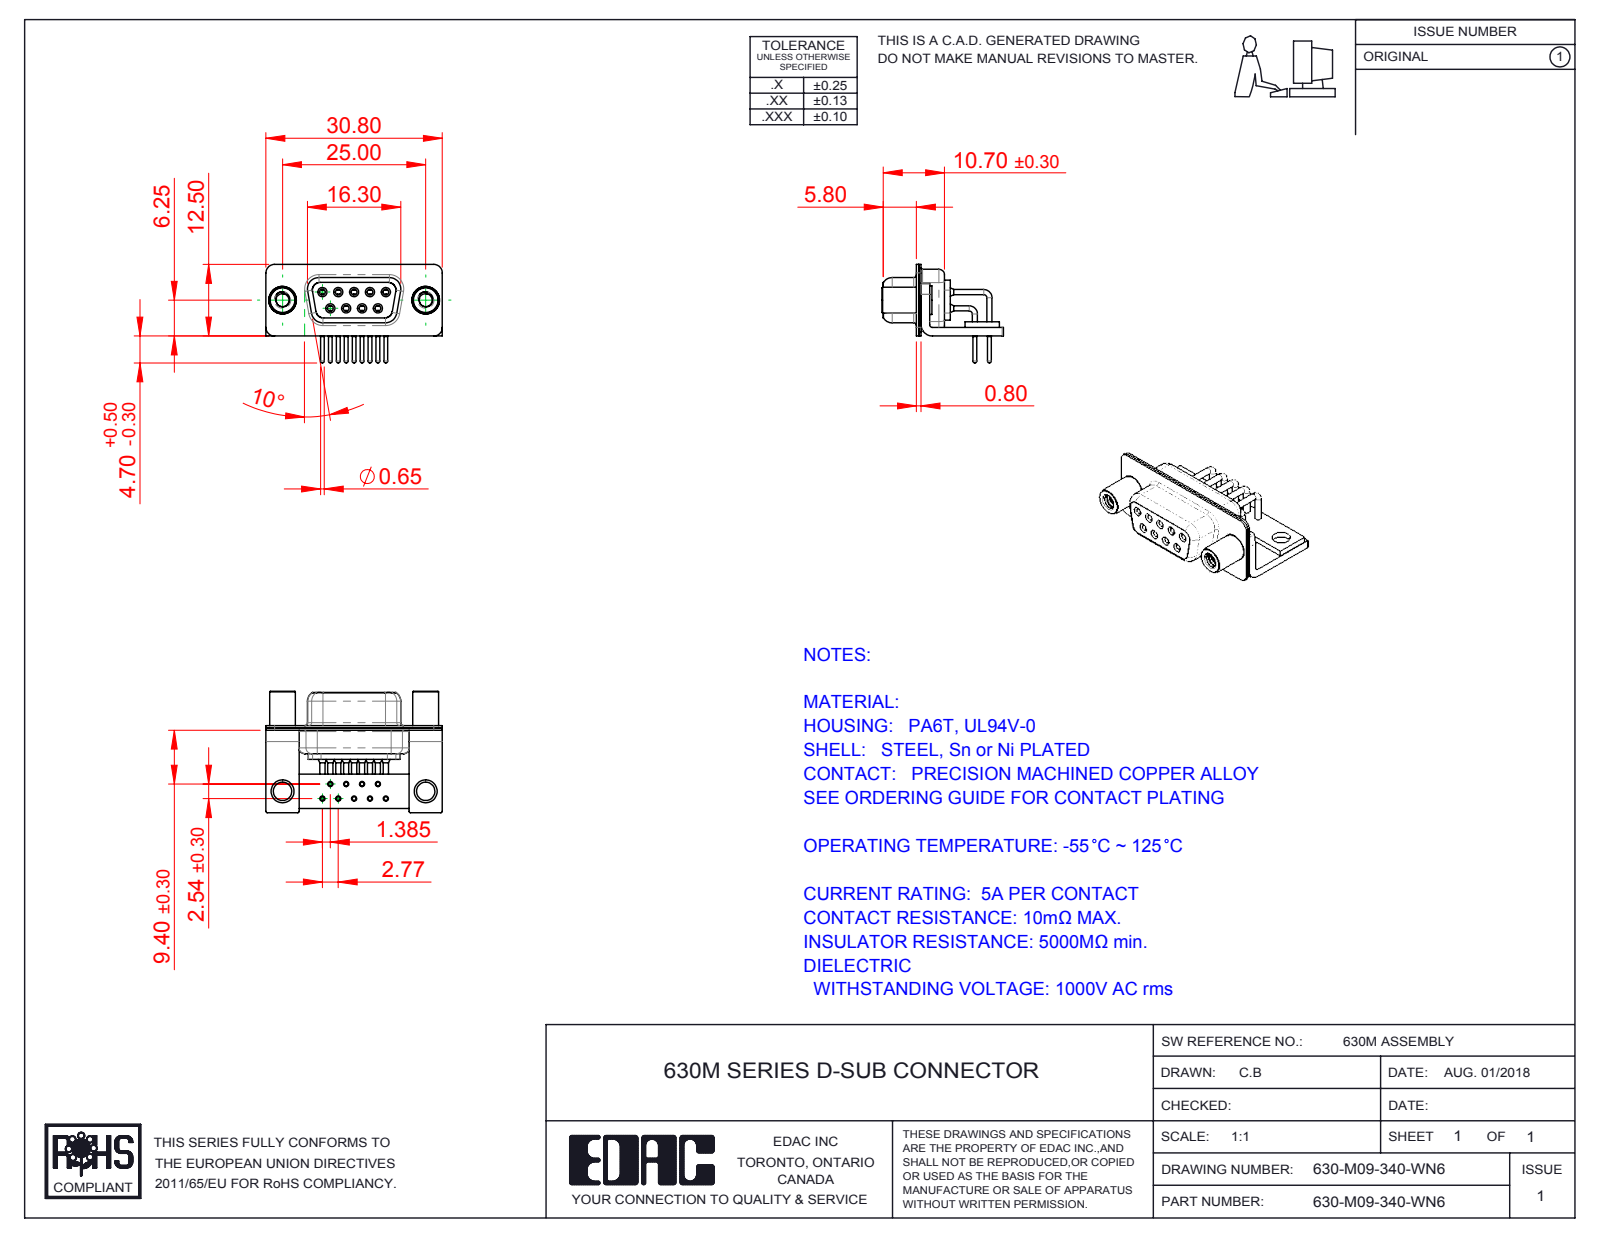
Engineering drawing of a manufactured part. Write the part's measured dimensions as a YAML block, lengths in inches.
part_name: "630M Shell Rear_09 Contacts; 630M Housing_09 Contacts; 630M 4-40 Threaded Standoff; 630M Stabilizer Board_09 Contacts (+5 more)"
step_written_by: "SolidWorks 2016 (CONFIG_CONTROL_DESIGN)"
units: inches
bodies: {solids: 17, faces: 874, planar: 230, cylindrical: 426, other: 218}
overall_size: [1.213, 0.835, 0.677]
volume: 0.141
surface_area: 9.292
round_holes:
  - {diameter: 0.035, count: 9}
  - {diameter: 0.039, count: 9}
  - {diameter: 0.043, count: 9}
  - {diameter: 0.067, count: 9}
  - {diameter: 0.071, count: 9}
  - {diameter: 0.079, count: 9}
  - {diameter: 0.089, count: 2}
  - {diameter: 0.126, count: 2}
  - {diameter: 0.157, count: 2}
  - {diameter: 0.189, count: 2}
round_bosses_or_shafts:
  - {diameter: 0.063, count: 9}
  - {diameter: 0.059, count: 9}
  - {diameter: 0.035, count: 9}
  - {diameter: 0.026, count: 9}
  - {diameter: 0.197, count: 2}
  - {diameter: 0.193, count: 2}
  - {diameter: 0.177, count: 2}
partial_cylinders:
  - {radius: 0.01, count: 16}
  - {radius: 0.059, count: 16}
  - {radius: 0.079, count: 13}
  - {radius: 0.053, count: 8}
  - {radius: 0.063, count: 8}
  - {radius: 0.02, count: 5}
  - {radius: 0.024, count: 4}
  - {radius: 0.026, count: 4}
face_to_face_distances: [0.016, 0.031, 0.059, 0.091, 0.075, 0.039, 0.368, 0.057, 0.335, 0.352]
hole_center_spacings: [0.109, 0.218, 0.124, 0.192, 0.327, 0.114, 0.114, 0.198]
